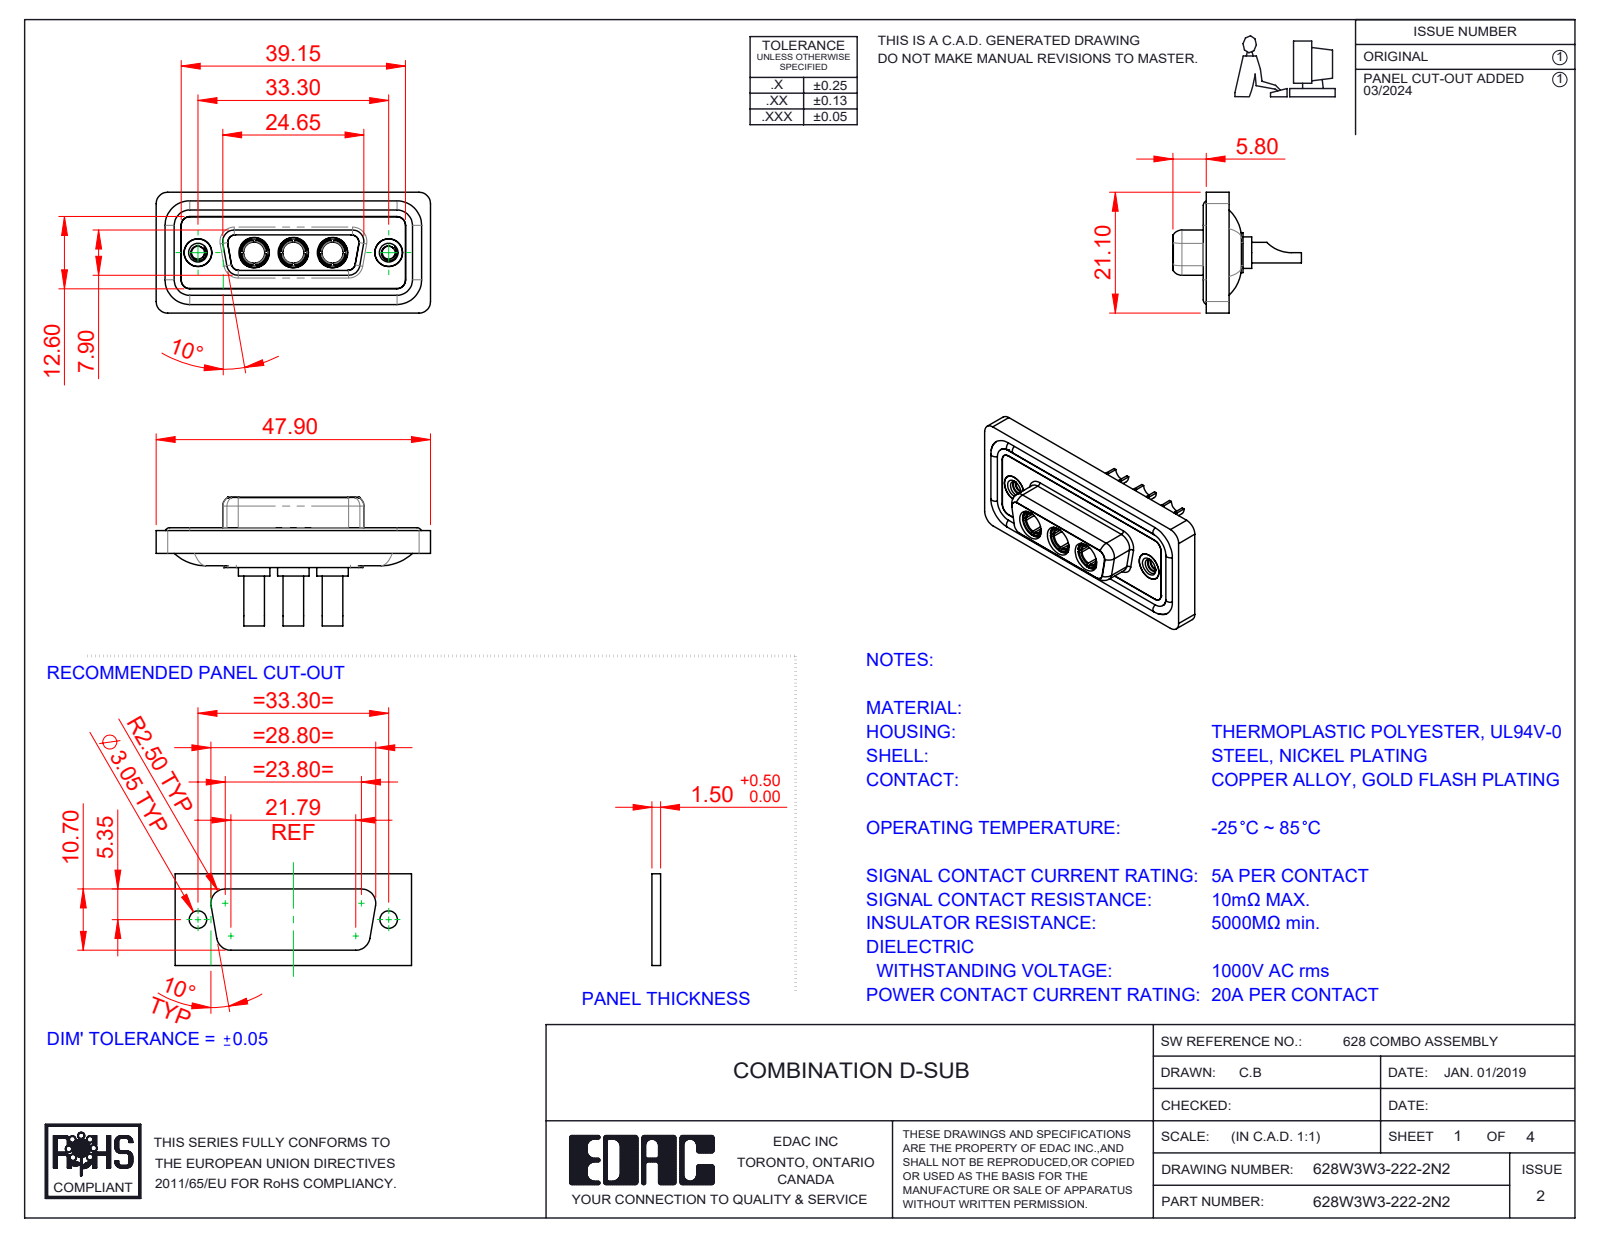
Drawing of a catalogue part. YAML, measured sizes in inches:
part_name: "628Combo Threaded Rivet_2; 628W3W3-222-2N2; 628Combo Housing_3W3; 628Combo Shell Rear_15 Contacts (+3 more)"
step_written_by: "SolidWorks 2023 (CONFIG_CONTROL_DESIGN)"
units: inches
bodies: {solids: 13, faces: 626, planar: 201, cylindrical: 266, other: 159}
overall_size: [1.886, 0.884, 0.831]
volume: 0.37
surface_area: 15.48
round_holes:
  - {diameter: 0.191, count: 5}
  - {diameter: 0.106, count: 3}
  - {diameter: 0.146, count: 3}
  - {diameter: 0.209, count: 3}
  - {diameter: 0.089, count: 2}
  - {diameter: 0.157, count: 2}
  - {diameter: 0.159, count: 2}
  - {diameter: 0.197, count: 2}
round_bosses_or_shafts:
  - {diameter: 0.063, count: 4}
  - {diameter: 0.217, count: 3}
  - {diameter: 0.205, count: 3}
  - {diameter: 0.195, count: 3}
  - {diameter: 0.187, count: 3}
  - {diameter: 0.148, count: 3}
  - {diameter: 0.142, count: 3}
  - {diameter: 0.195, count: 2}
partial_cylinders:
  - {radius: 0.059, count: 22}
  - {radius: 0.079, count: 20}
  - {radius: 0.053, count: 12}
  - {radius: 0.063, count: 8}
  - {radius: 0.01, count: 4}
  - {radius: 0.02, count: 4}
  - {radius: 0.024, count: 4}
  - {radius: 0.026, count: 4}
face_to_face_distances: [0.016, 0.071, 0.063, 0.02, 0.293, 0.043, 0.114, 0.222, 0.278, 0.26]
hole_center_spacings: [0.27, 0.386, 0.656, 0.925, 0.539, 1.311]
